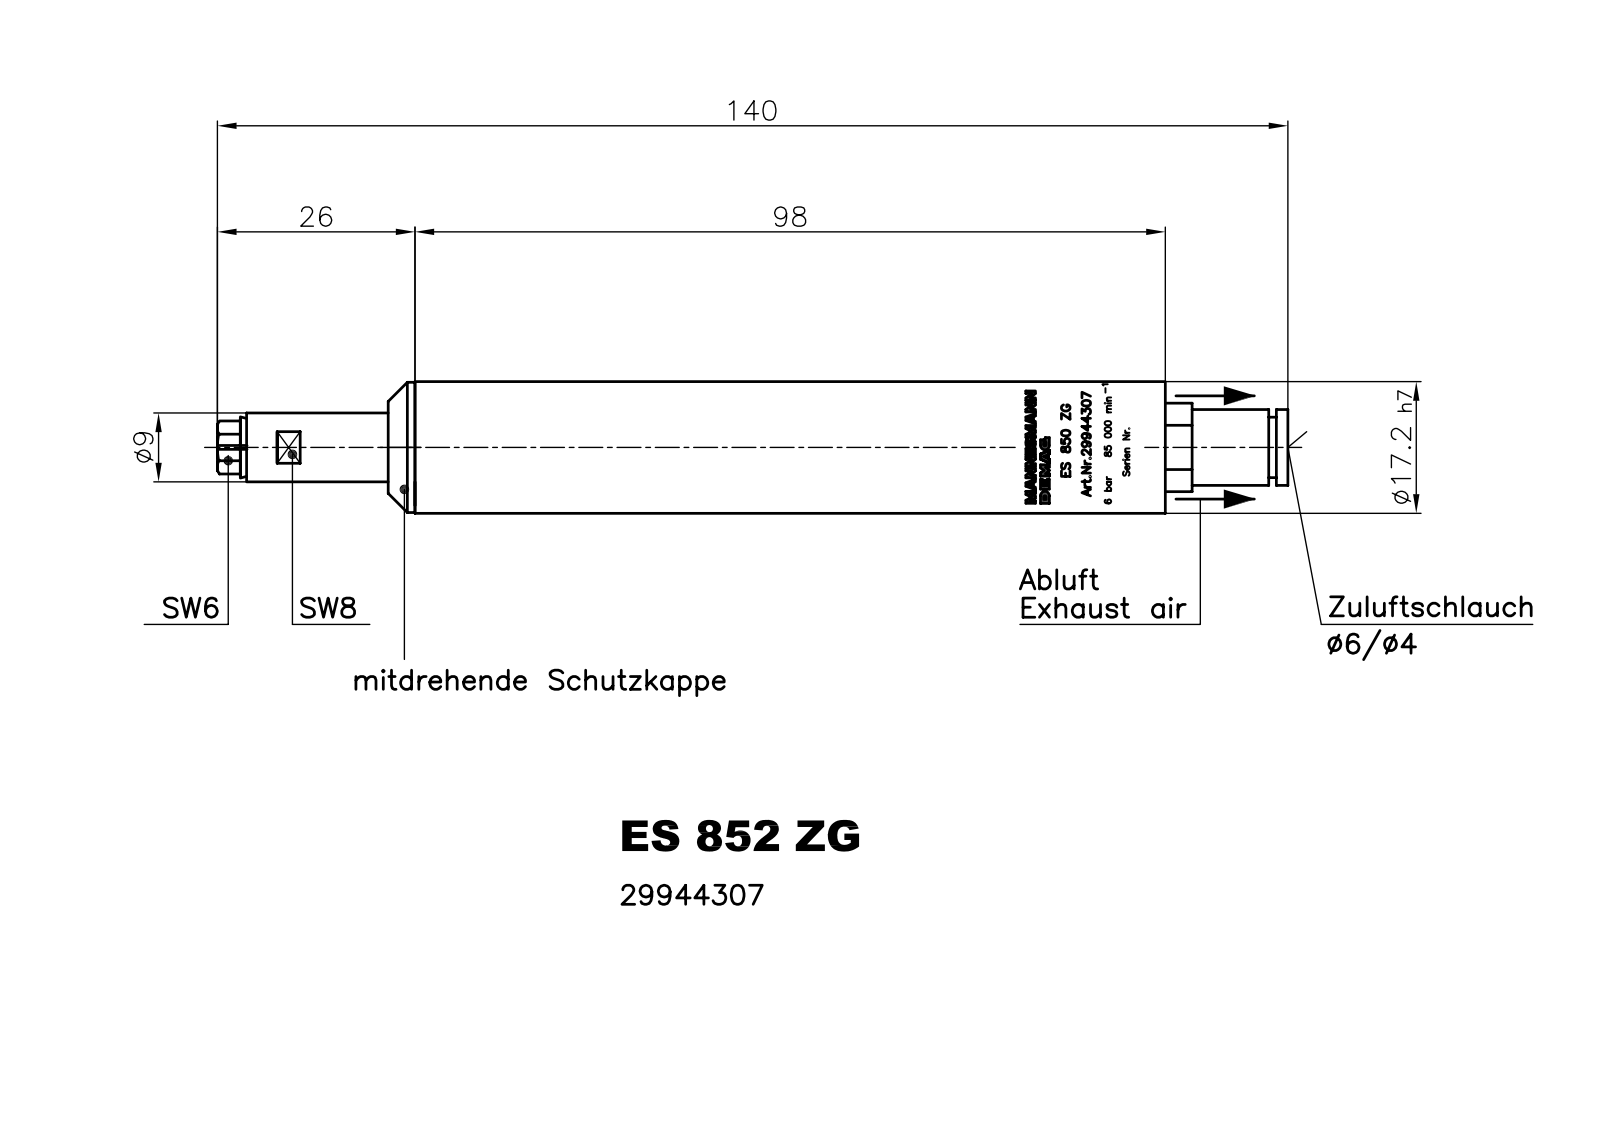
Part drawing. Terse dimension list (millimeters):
name: ES 852 ZG_29944307
written by: Autodesk Inventor 2008 (CONFIG_CONTROL_DESIGN)
unit: mm
bodies: 1 solid, 126 faces (65 planar, 28 cylindrical, 33 other)
size: 139.81 × 17.2 × 17.2
volume: 25 383 mm³; area: 7 733 mm²
holes: 1× ⌀3, 1× ⌀3.1, 1× ⌀6
bosses: 1× ⌀17.2, 1× ⌀17, 1× ⌀16.19, 1× ⌀16, 1× ⌀9.9, 1× ⌀9, 1× ⌀7.2
rounds: 4× R5, 1× R2.5, 1× R5.5
face distances: 4.75, 5.25, 9.48, 10, 1.74, 7.74, 0.5, 101.9, 98.2, 117.7
